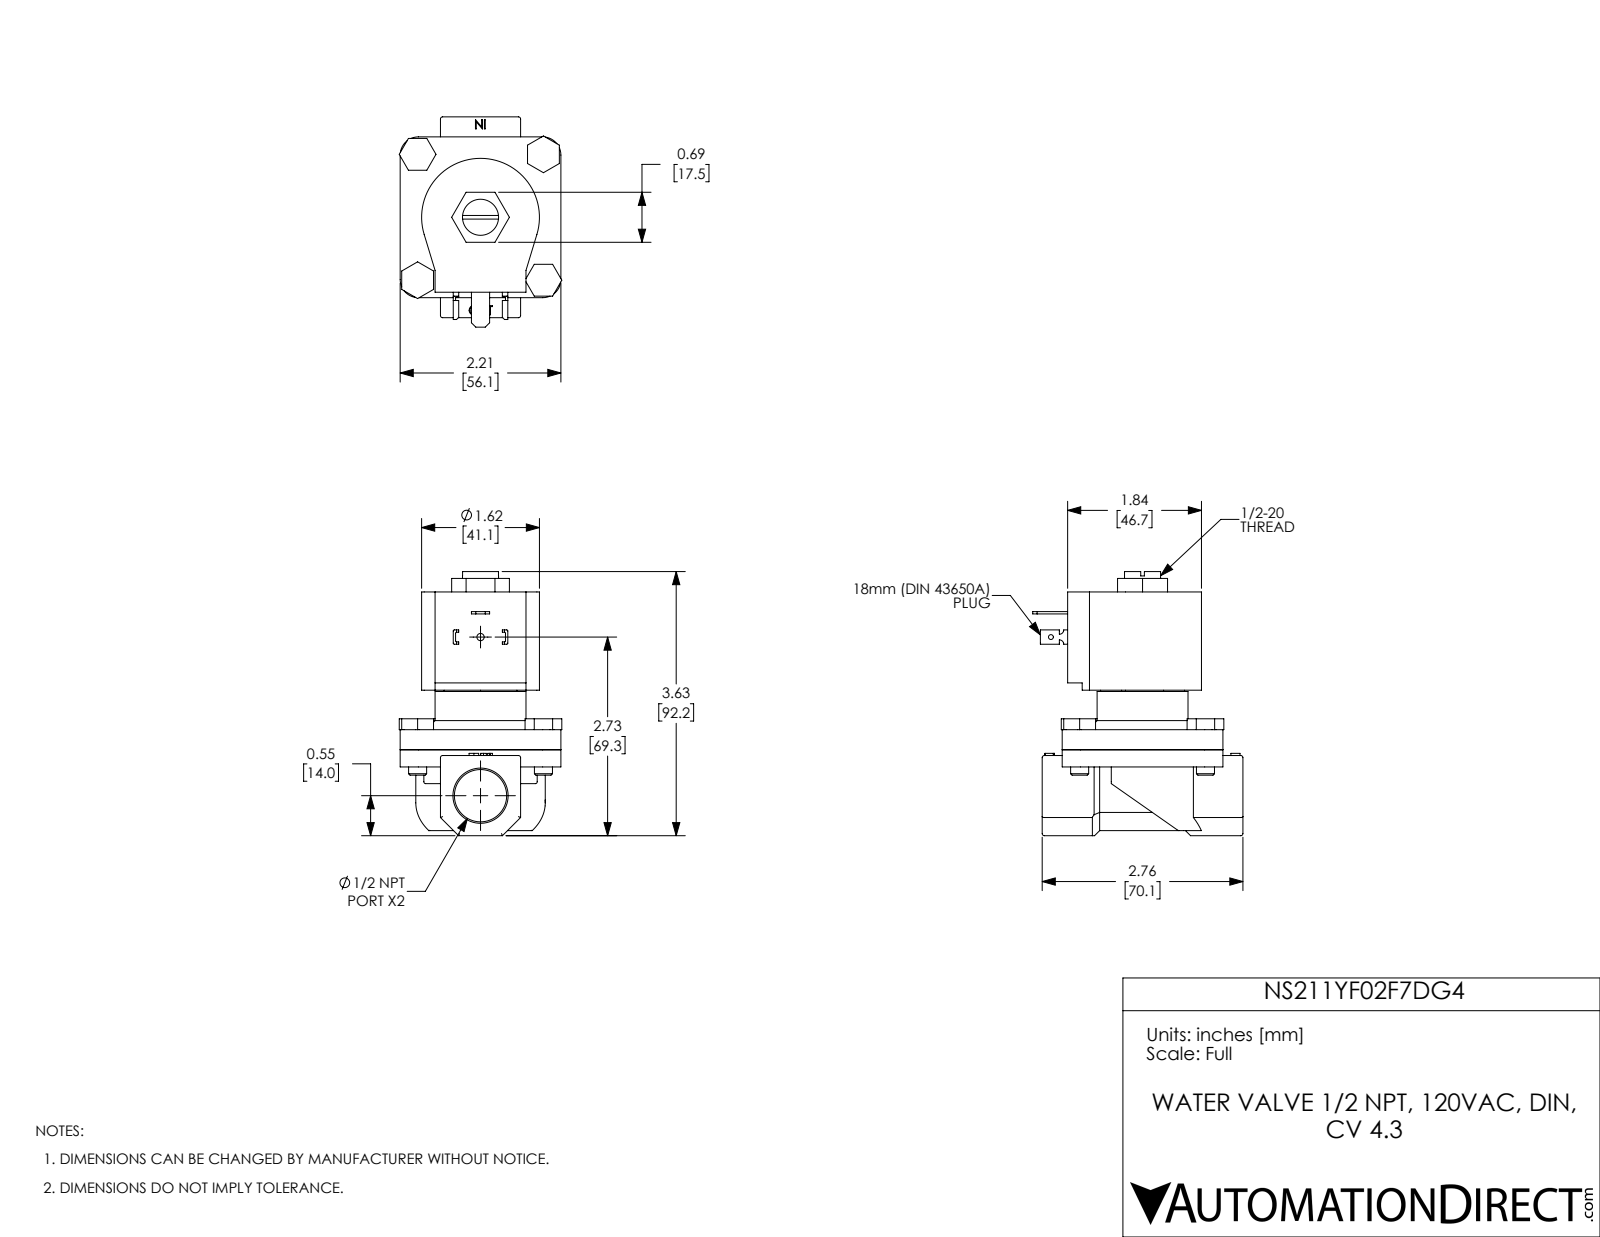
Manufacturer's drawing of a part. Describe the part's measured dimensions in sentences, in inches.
The part is named "NS211YF02F7DG4". Its 3-D file was written by "SolidWorks 2017 (AUTOMOTIVE_DESIGN)". It is 11 solids with 330 faces: 196 planar, 99 cylindrical and 35 other. Overall it measures 3.63 by 2.89 by 2.235 inches. Its volume is 9.198 cubic inches and its surface area 60.98 square inches. Round holes: 4 of diameter 0.25, 1 of diameter 0.067, 1 of diameter 0.1, 1 of diameter 0.496, 1 of diameter 0.512, 1 of diameter 0.719, 1 of diameter 1.155. Round bosses or shafts: 4 of diameter 0.248, 1 of diameter 1.25. Partial cylindrical surfaces (rounded edges, fillets, slot ends): 15 of radius 0.03, 8 of radius 0.015, 4 of radius 0.25, 2 of radius 0.06, 1 of radius 0.81, 1 of radius 0.89. The main face-to-face distances are 0.276, 2.169, 1.893, 0.554, 1.656, 0.236, 0.512, 2.405, 2.21, 1.102. The hole center spacings are 1.223, 1.73, 2.446, 2.18.
